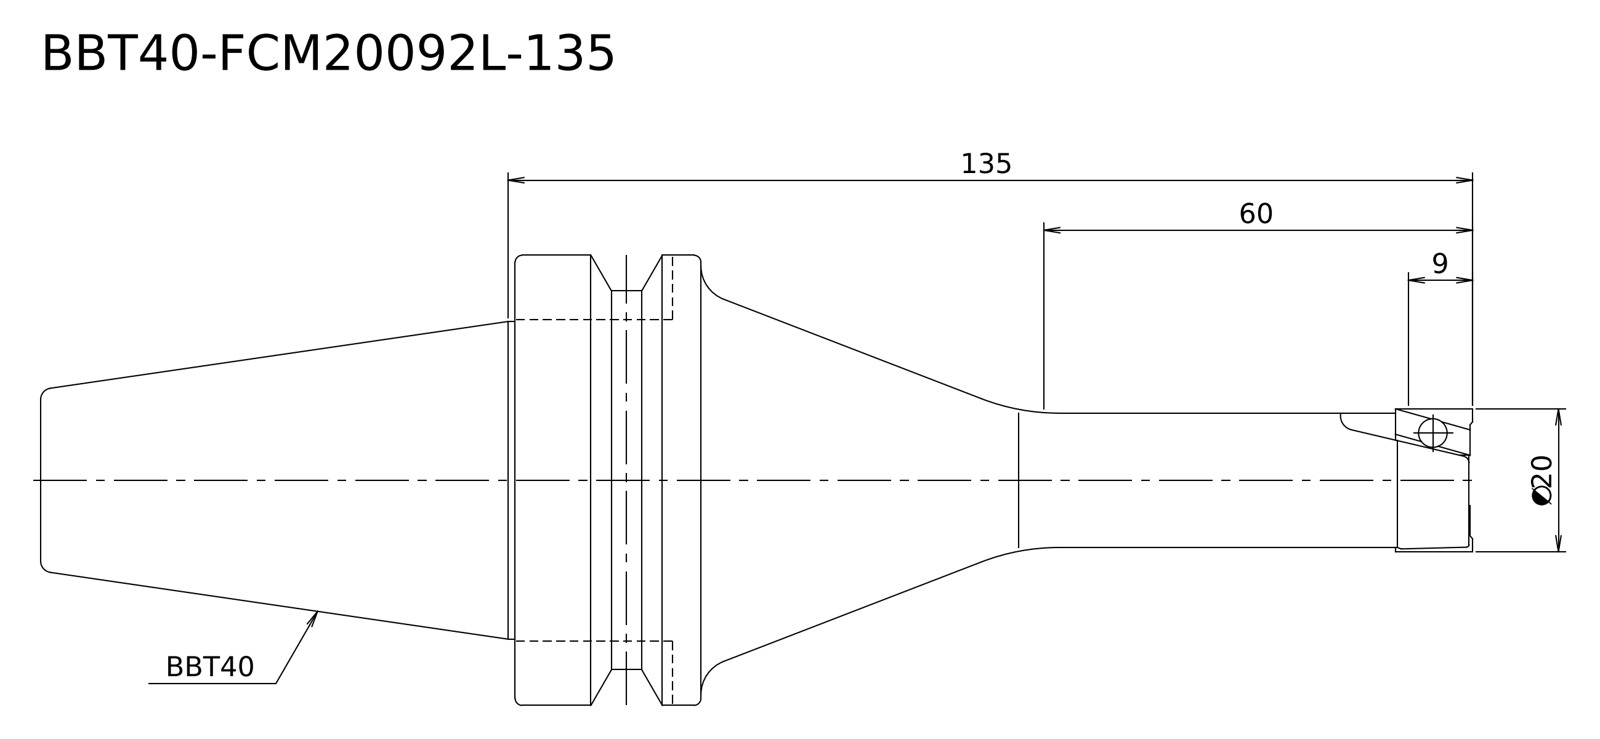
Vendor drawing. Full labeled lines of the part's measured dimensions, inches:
STEP written by: Kubotek KeyCreator V8.5.1 (14335) (CONFIG_CONTROL_DESIGN)
Units: inches
Bodies: 1 solid, 17 faces (4 planar, 6 cylindrical, 7 other)
Overall size (bounding box): 7.89 × 2.48 × 2.48
Volume: 12.7 in³ · Surface area: 39.79 in²
Round bosses / shafts (diameter × count): ⌀2.48 ×1, ⌀2.087 ×1, ⌀1.75 ×1, ⌀0.787 ×1, ⌀0.74 ×1
Main face-to-face distances: 2.614, 5.276, 7.89, 4.252, 1.024, 3.638
